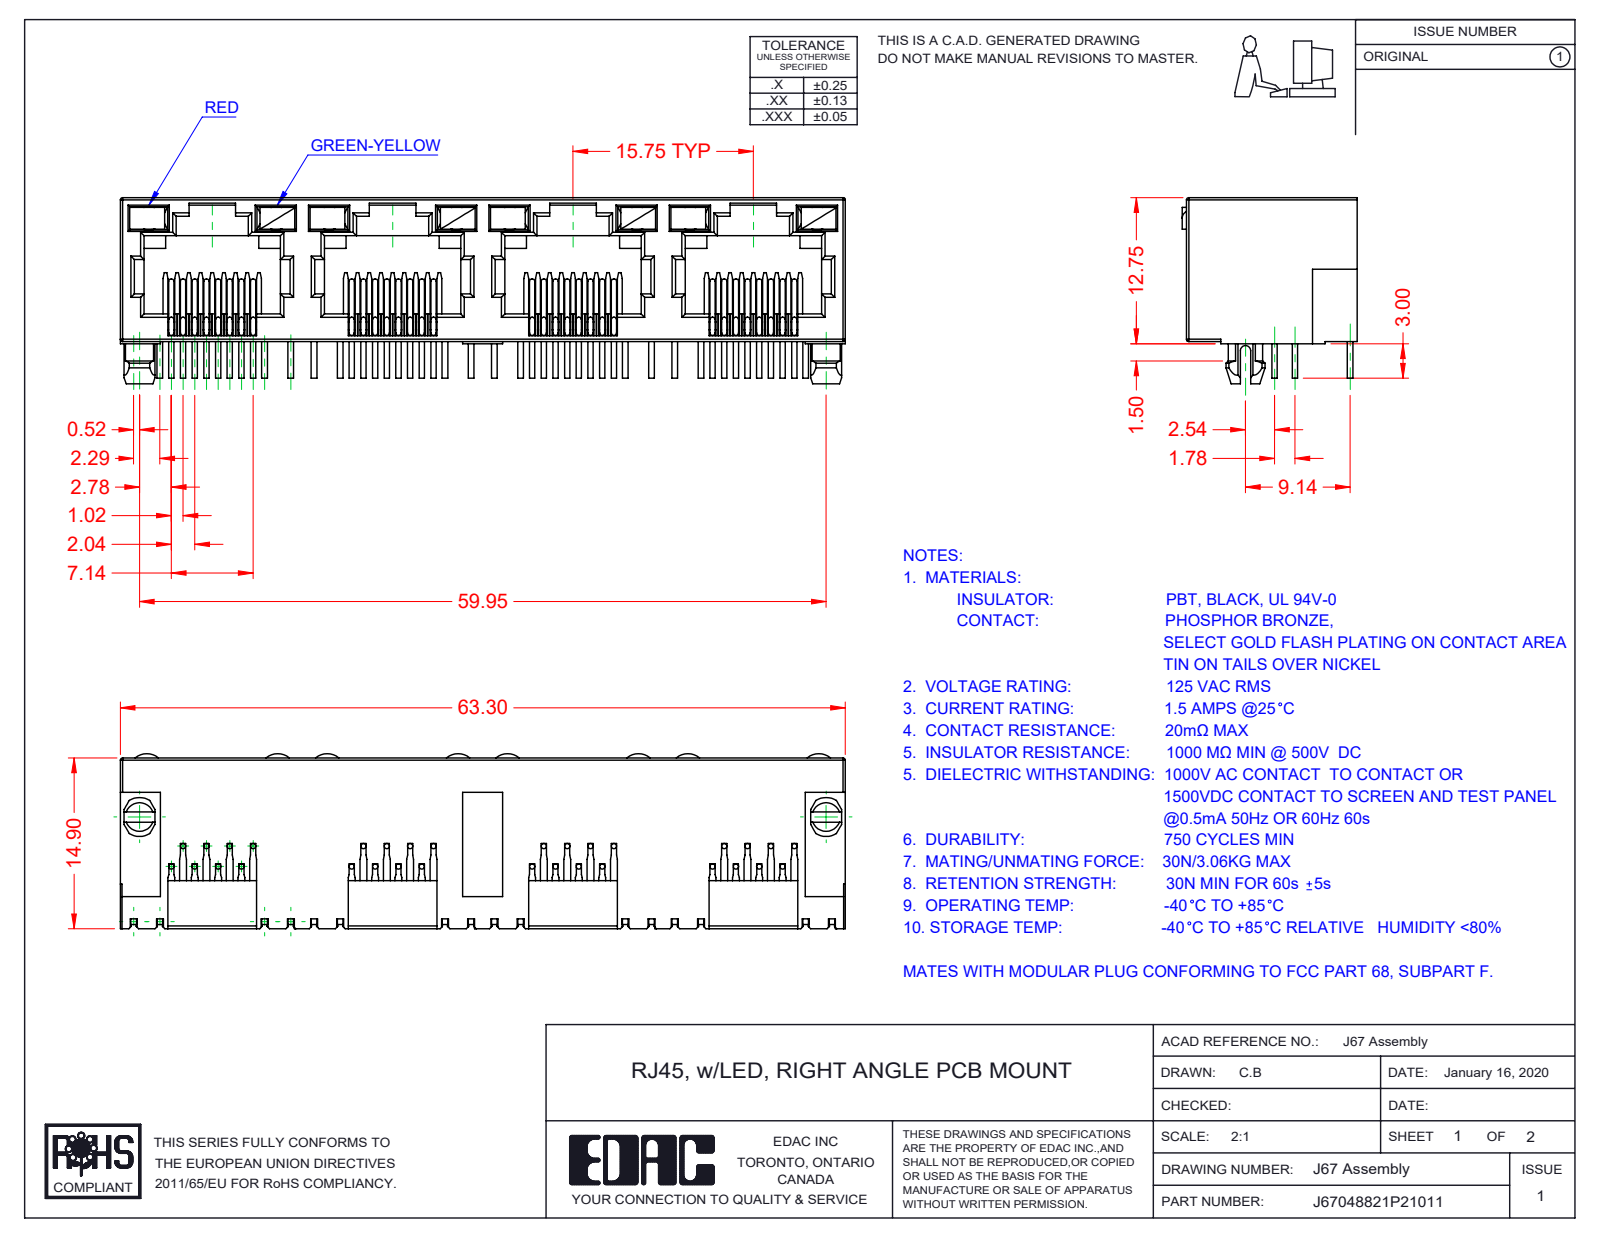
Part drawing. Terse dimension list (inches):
name: 67 Insulator; 67 LED RH_5-Green-Yellow; 67 Contacts; J67048822P25011 (+1 more)
written by: SolidWorks 2016 (CONFIG_CONTROL_DESIGN)
unit: in
bodies: 41 solids, 2473 faces (1781 planar, 484 cylindrical, 208 other)
size: 2.492 × 0.64 × 0.602
volume: 0.315 in³; area: 17.94 in²
bosses: 96× ⌀0.018
rounds: 66× R0.008, 29× R0.012, 9× R0.018, 8× R0.061, 2× R0.059, 2× R0.067, 1× R0.014, 1× R0.039
face distances: 0.02, 0.494, 0.074, 0.035, 0.394, 0.62, 0.039, 0.055, 0.433, 0.468
